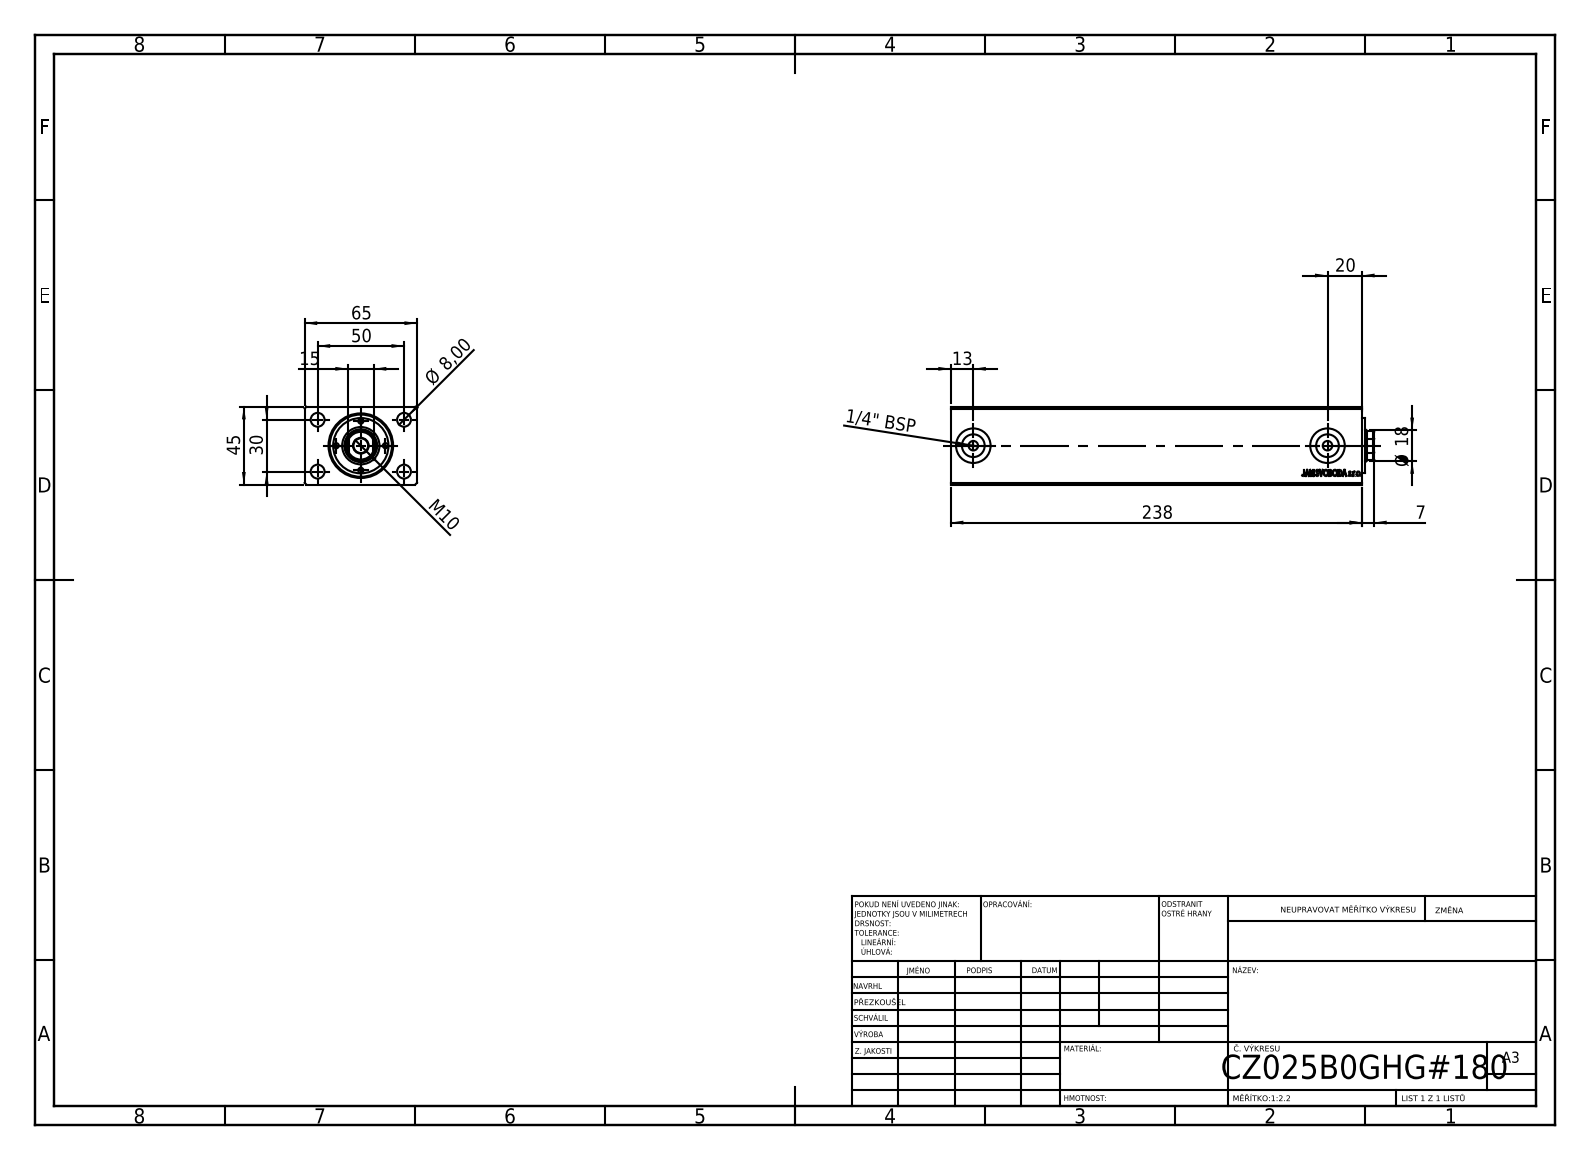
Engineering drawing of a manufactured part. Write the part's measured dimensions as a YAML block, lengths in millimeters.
part_name: "V500CZ_B_VC; V500CZ"
step_written_by: "SolidWorks 2019 (CONFIG_CONTROL_DESIGN)"
units: millimeters
bodies: {solids: 3, faces: 873, planar: 399, cylindrical: 58, other: 416}
overall_size: [245, 65, 45]
volume: 638862
surface_area: 99981
round_holes:
  - {diameter: 3, count: 4}
  - {diameter: 8, count: 4}
  - {diameter: 5.5, count: 2}
  - {diameter: 13.16, count: 2}
  - {diameter: 20, count: 2}
  - {diameter: 8.5, count: 1}
  - {diameter: 18, count: 1}
  - {diameter: 19, count: 1}
  - {diameter: 25, count: 1}
  - {diameter: 36, count: 1}
round_bosses_or_shafts:
  - {diameter: 32, count: 1}
partial_cylinders:
  - {radius: 8.5, count: 1}
face_to_face_distances: [45, 65, 238, 7, 237.8, 225.2, 12.6, 12.8, 1.8, 5.2]
hole_center_spacings: [14.25, 18.45, 20.15, 25.01, 29.15, 38.48, 42.02, 28.5]
